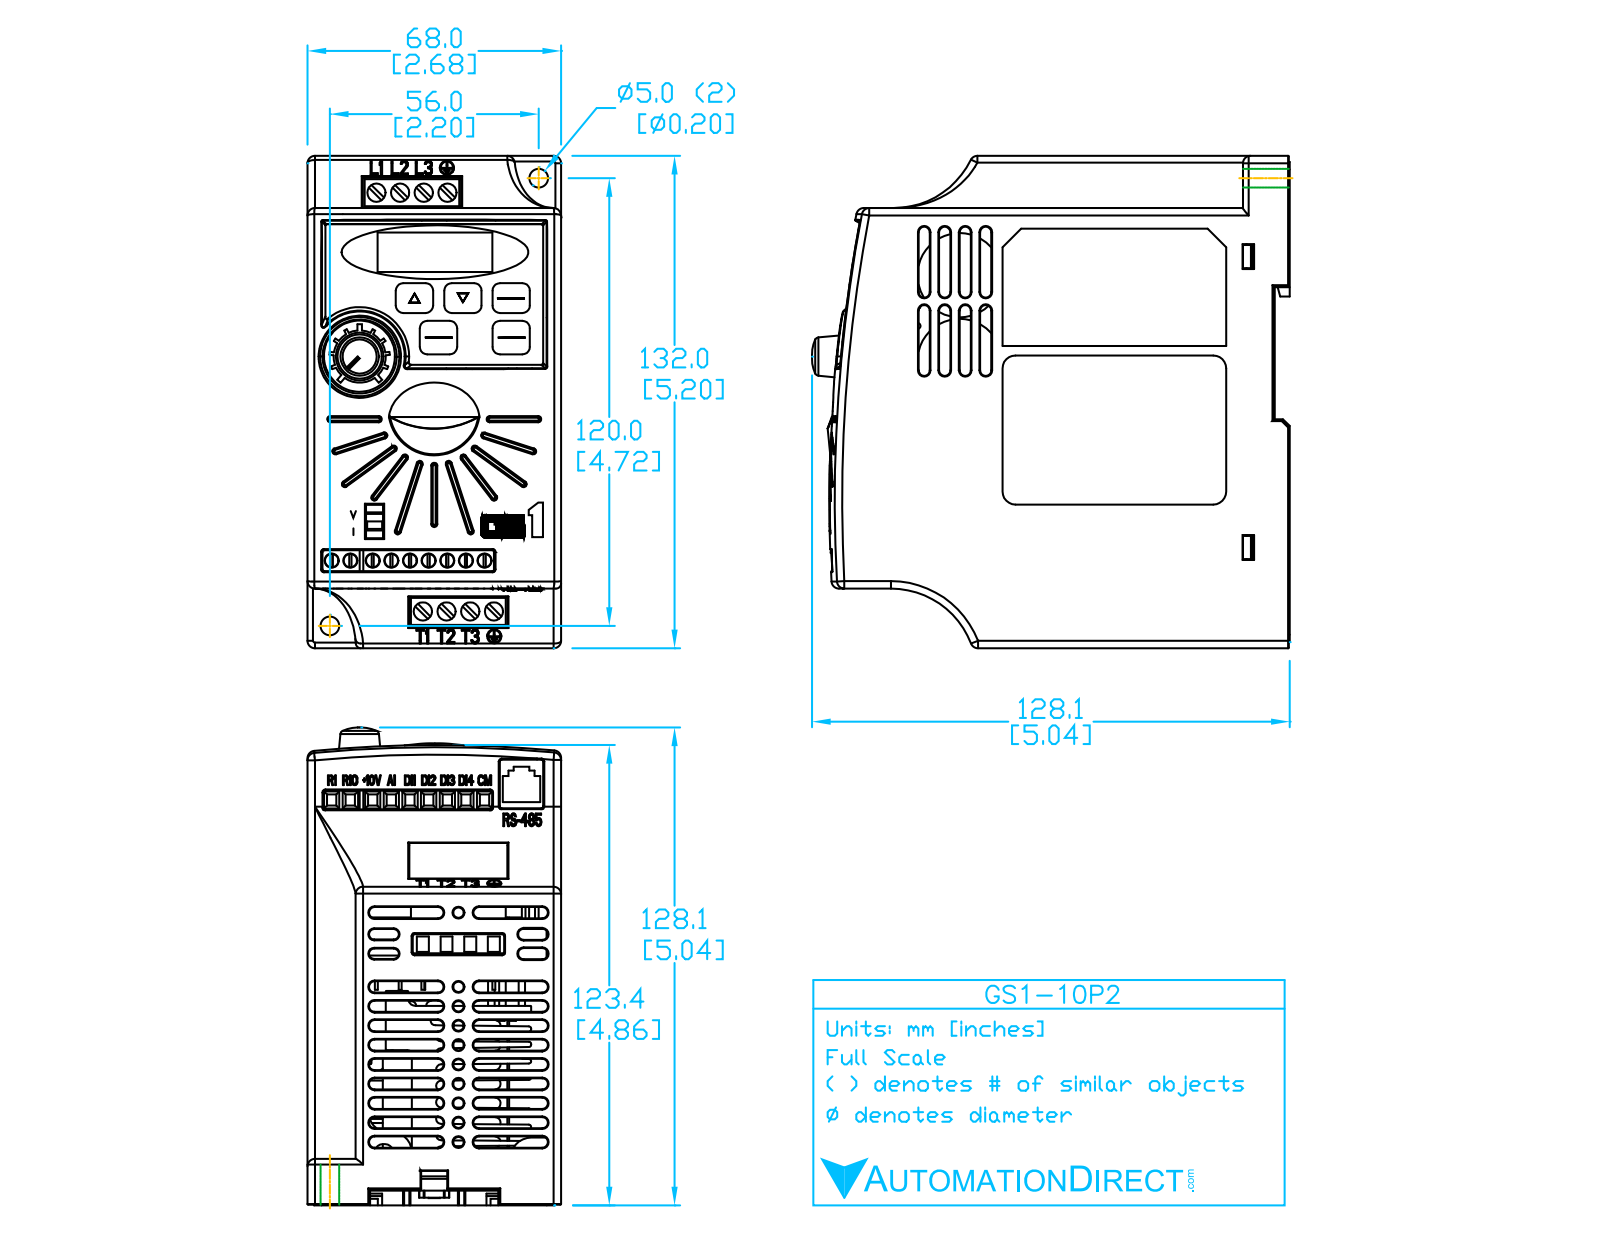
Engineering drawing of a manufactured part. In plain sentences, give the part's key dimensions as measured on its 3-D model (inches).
The part is named "GS1-10P2". Its 3-D file was written by "SolidWorks 2013 (AUTOMOTIVE_DESIGN)". It is 1 solid with 884 faces: 549 planar, 168 cylindrical and 167 other. Overall it measures 5.285 by 5.2 by 2.68 inches. Its volume is 61.51 cubic inches and its surface area 109.5 square inches. Round holes: 9 of diameter 0.15, 8 of diameter 0.187, 2 of diameter 0.2. Round bosses or shafts: 5 of diameter 0.316. Partial cylindrical surfaces (rounded edges, fillets, slot ends): 38 of radius 0.03, 22 of radius 0.1, 20 of radius 0.06, 6 of radius 0.063, 2 of radius 0.015, 2 of radius 0.093, 2 of radius 0.2, 2 of radius 0.44. The main face-to-face distances are 2.68, 0.175, 5.2, 0.015, 5.185, 0.167, 0.55, 4.65, 0.535, 0.62. The hole center spacings are 0.2, 0.4, 0.6, 0.8, 1, 1.2, 1.4, 3.921.
